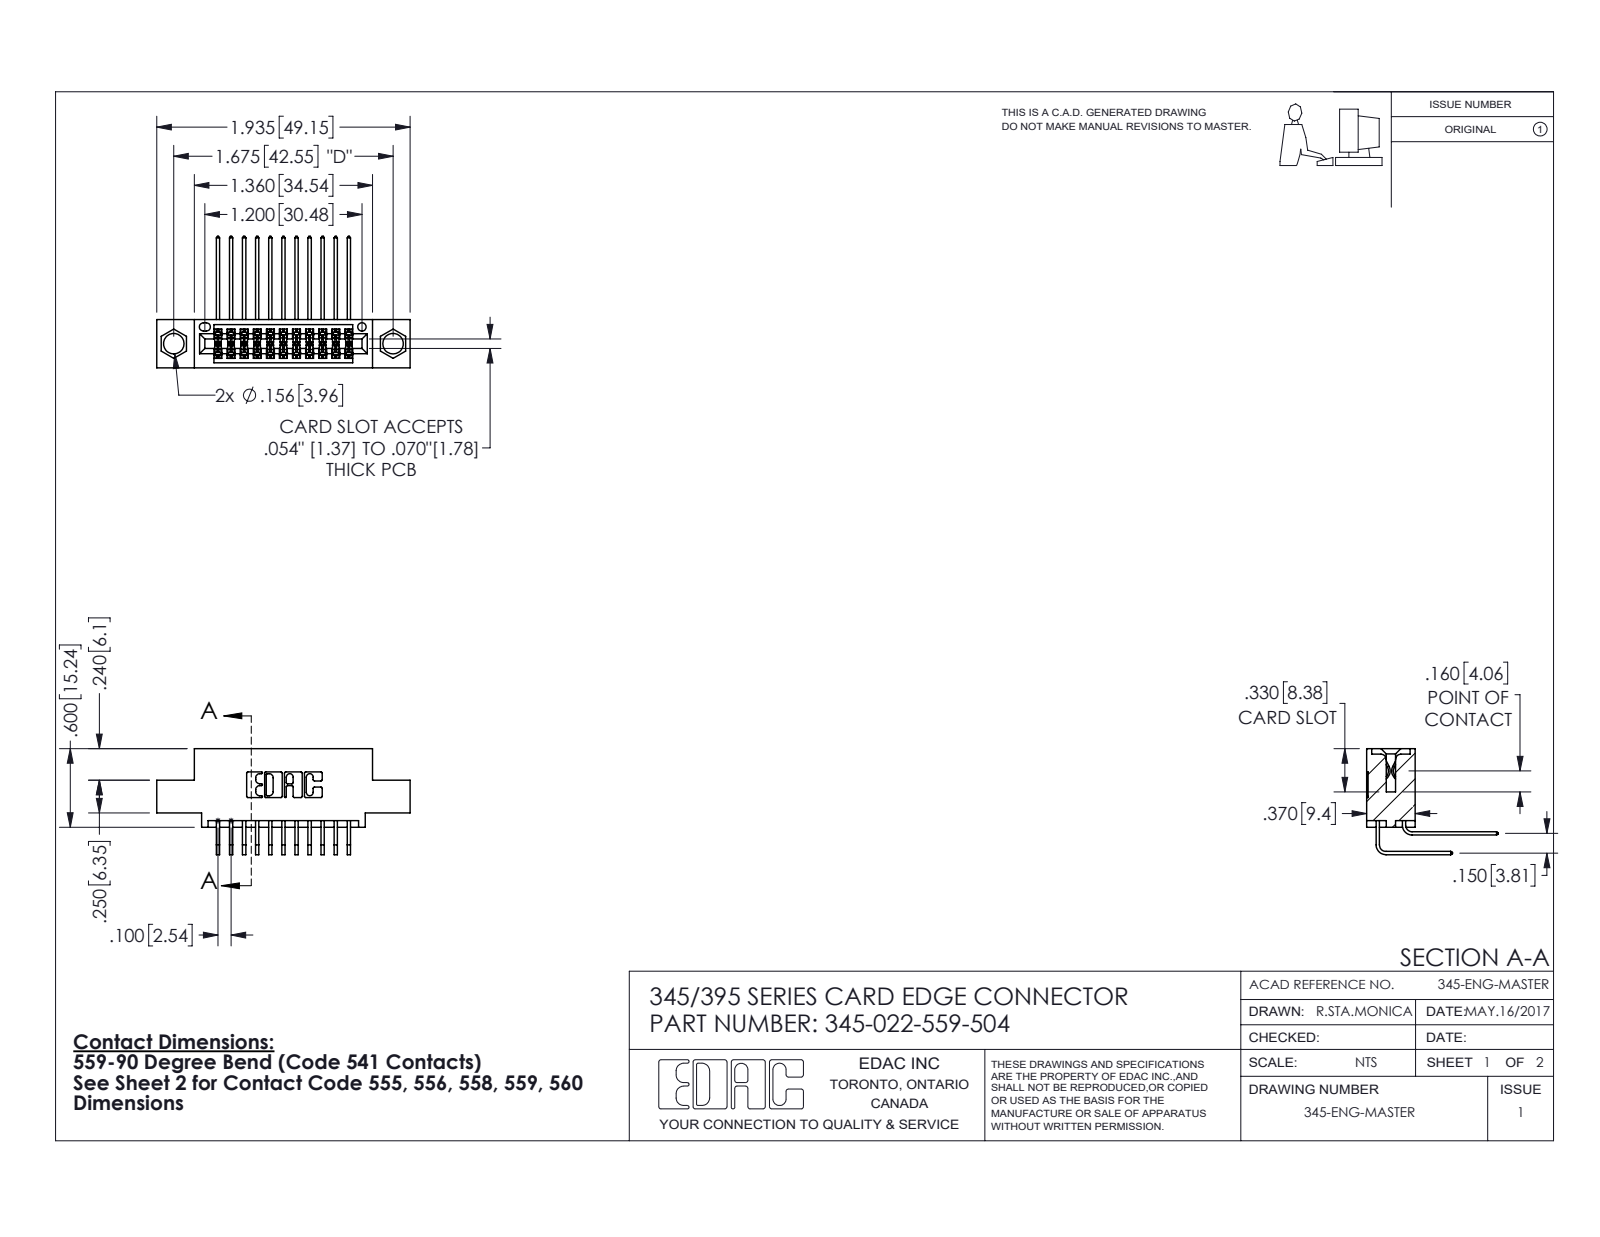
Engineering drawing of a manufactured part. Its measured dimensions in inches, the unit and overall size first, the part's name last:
Units: inches
Overall size (bounding box): 1.935 × 1.005 × 0.809
Round holes (diameter × count): ⌀0.156 ×2, ⌀0.064 ×1
Partial cylindrical surfaces — rounded edges, fillets, slot ends (radius × count): R0.006 ×33, R0.01 ×22, R0.007 ×6, R0.031 ×6, R0.026 ×3, R0.014 ×2, R0.019 ×2, R0.022 ×2
Main face-to-face distances: 0.072, 0.298, 0.2, 0.37, 0.098, 0.272, 0.025, 0.15, 0.225, 0.1
Hole centre spacings: 0.27, 1.443, 1.675
Volume: 0.271 in³ · Surface area: 10.07 in²
Bodies: 23 solids, 1288 faces (868 planar, 420 cylindrical, 0 other)
Part name (STEP PRODUCT): 345-022-559-504; 345 Part_0.110 Offset - 0.156 Dia-TI; 345-292-001_559 Tail - 2; 345-292-001_558 559 Tail - 1
STEP written by: SolidWorks 2020 (CONFIG_CONTROL_DESIGN)
